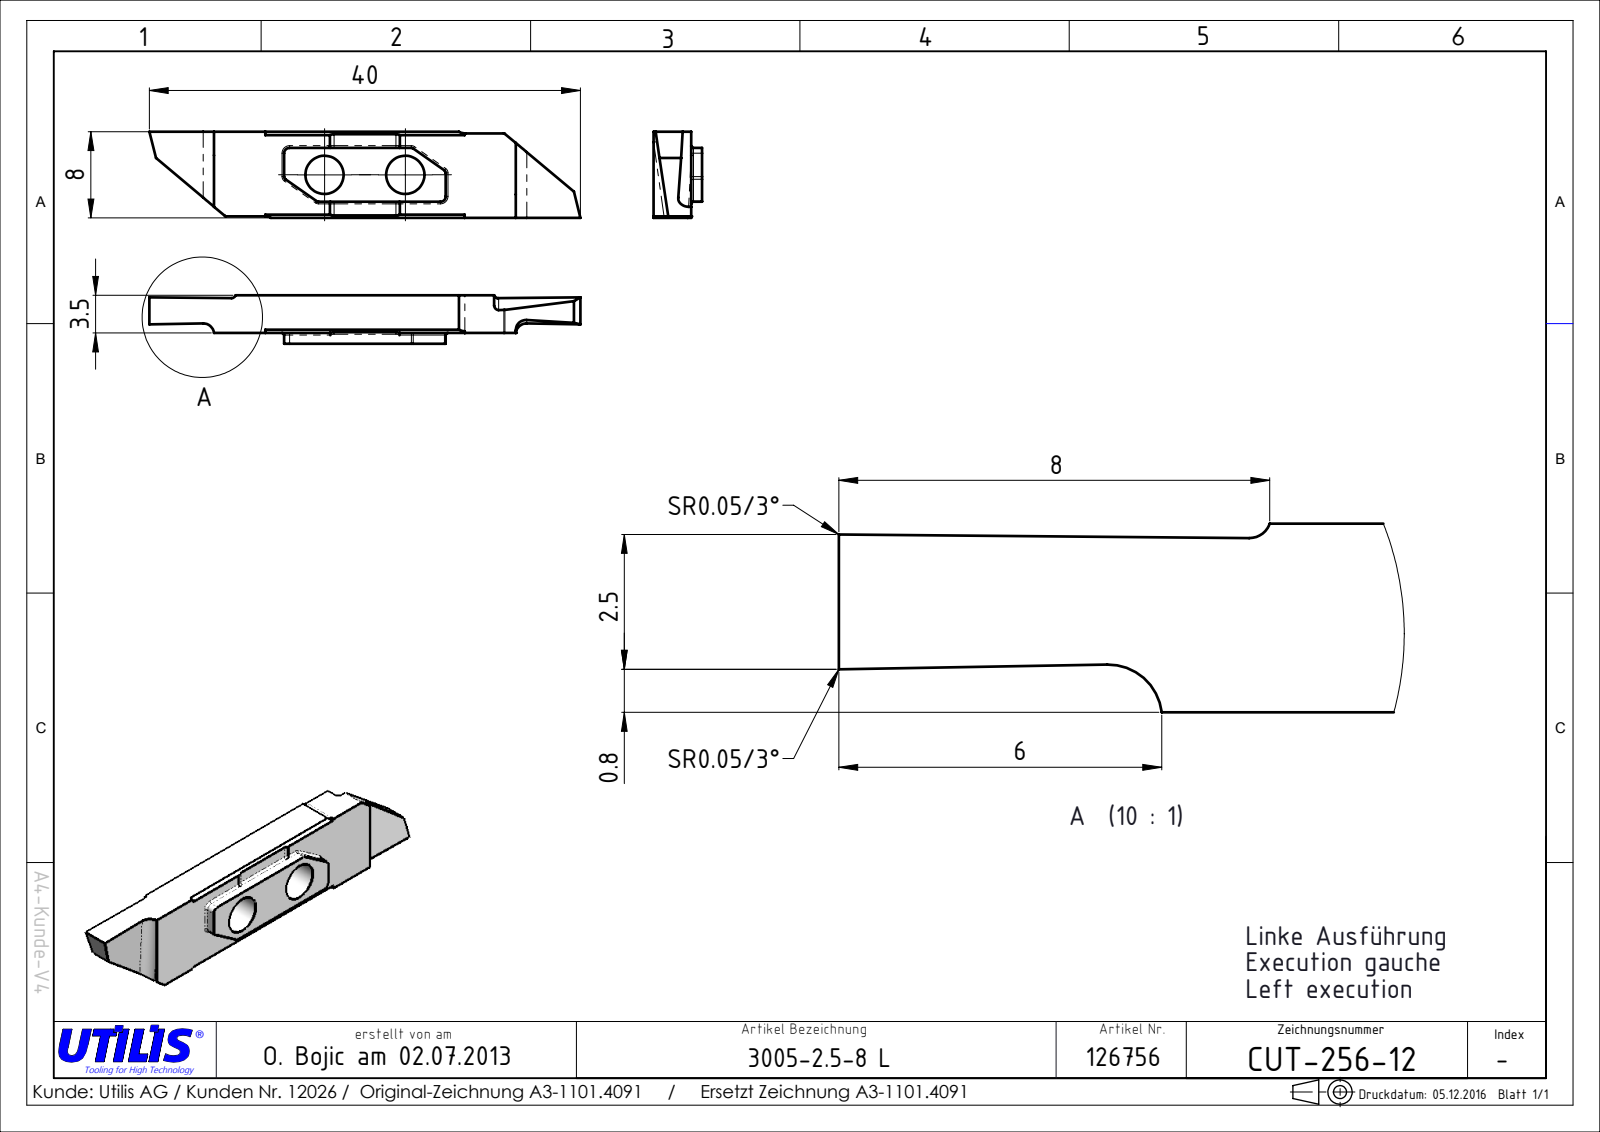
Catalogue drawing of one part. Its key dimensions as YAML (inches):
part_name: "CUT-256-12"
step_written_by: "SolidWorks 2016 (AUTOMOTIVE_DESIGN)"
units: inches
bodies: {solids: 1, faces: 36, planar: 22, cylindrical: 14, other: 0}
overall_size: [1.575, 0.315, 0.138]
volume: 0.051
surface_area: 1.34
round_holes:
  - {diameter: 0.14, count: 2}
partial_cylinders:
  - {radius: 0.006, count: 4}
  - {radius: 0.039, count: 4}
  - {radius: 0.016, count: 2}
face_to_face_distances: [0.138, 0.315, 0.309, 0.887, 0.303, 1.575, 1.535, 0.423, 1.152, 0.728]
hole_center_spacings: [0.295]
